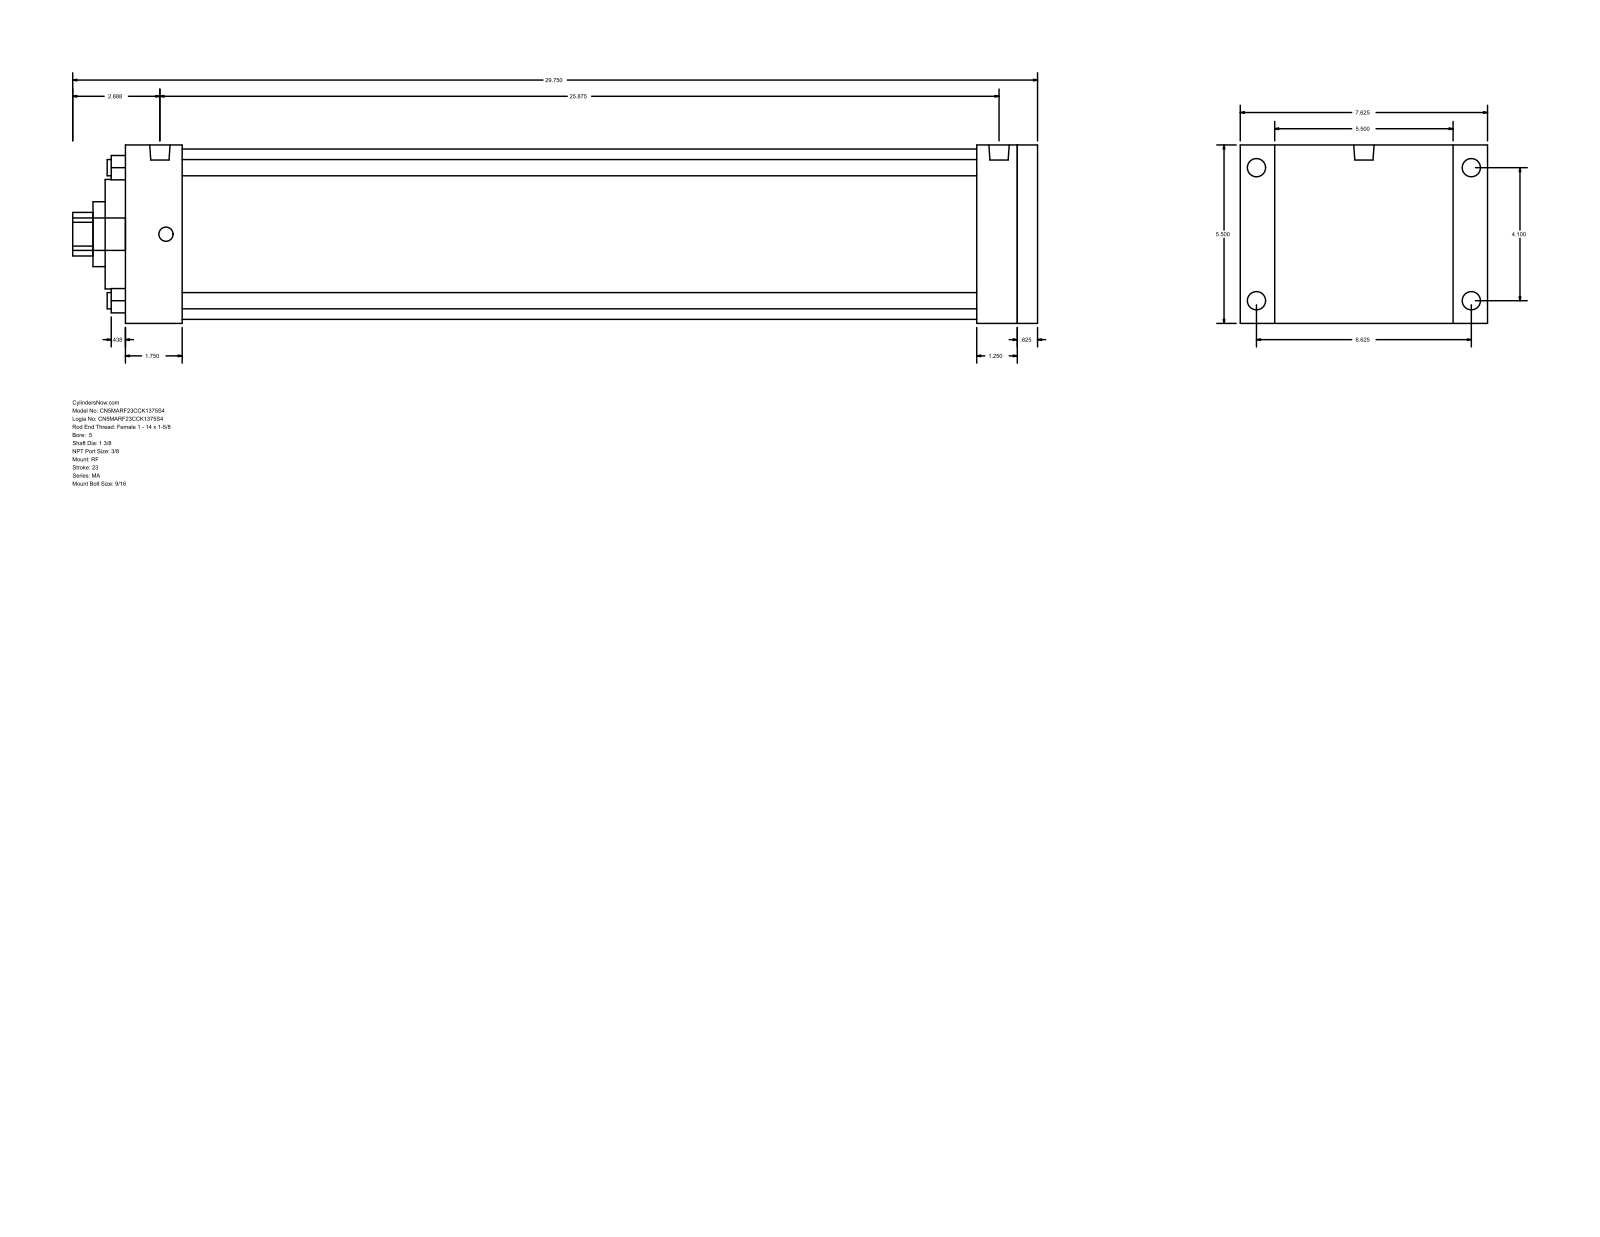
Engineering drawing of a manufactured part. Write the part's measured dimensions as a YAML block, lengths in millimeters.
part_name: "MA_RF__0500_1.375"
step_written_by: "GSSL Pune (CONFIG_CONTROL_DESIGN)"
units: millimeters
bodies: {solids: 0, faces: 94, planar: 65, cylindrical: 29, other: 0}
overall_size: [755.65, 193.68, 139.7]
round_holes:
  - {diameter: 12.7, count: 4}
  - {diameter: 34.92, count: 1}
  - {diameter: 50.8, count: 1}
  - {diameter: 85.72, count: 1}
  - {diameter: 133.35, count: 1}
round_bosses_or_shafts:
  - {diameter: 14.29, count: 4}
  - {diameter: 11.11, count: 4}
  - {diameter: 15.93, count: 2}
  - {diameter: 25.4, count: 1}
partial_cylinders:
  - {radius: 17.06, count: 1}
face_to_face_distances: [139.7, 714.38, 15.88, 698.5, 44.45, 654.05, 669.93, 666.75, 622.3, 31.75]
hole_center_spacings: [73.64, 104.14, 147.28]
